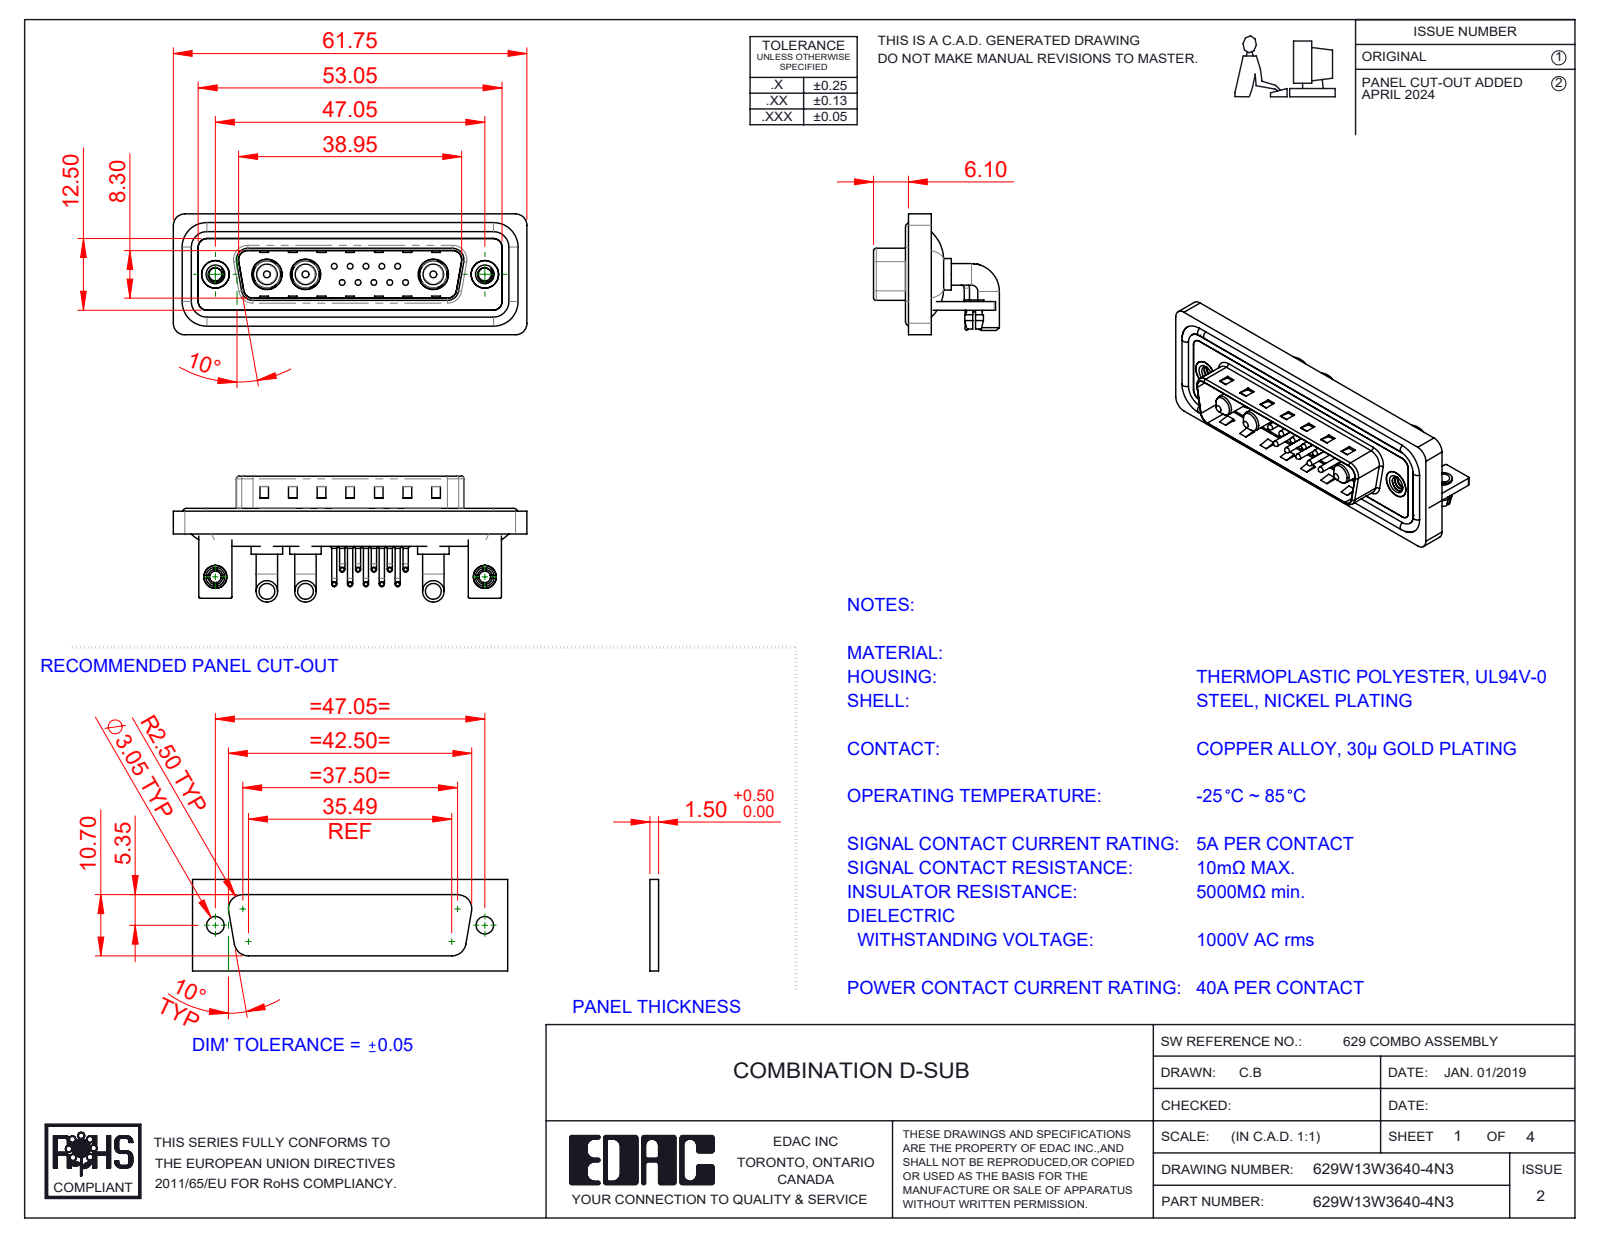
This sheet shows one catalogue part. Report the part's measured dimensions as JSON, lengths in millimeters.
{"part_name": "629Combo Contact Row 2; 629Combo Shell Rear_25 Contacts; Power Pin_40A RA; 629Combo Stabilizer Bracket (+7 more)", "step_written_by": "SolidWorks 2023 (CONFIG_CONTROL_DESIGN)", "units": "millimeters", "bodies": {"solids": 27, "faces": 1844, "planar": 947, "cylindrical": 661, "other": 236}, "overall_size": [61.75, 21.98, 21.1], "volume_mm3": 8143, "surface_area_mm2": 13425, "round_holes": [[2, 12], [0.75, 10], [1.6, 10], [4.85, 3], [5.3, 3], [2.26, 2], [2.5, 2], [3.2, 2], [4, 2], [4.8, 2], [5, 2]], "round_bosses_or_shafts": [[0.9, 20], [1.5, 10], [1, 10], [0.65, 10], [3.75, 6], [1.6, 4], [5.5, 3], [5.2, 3]], "partial_cylinders_radius": [[2, 19], [1.5, 18], [0.25, 16], [1.01, 10], [0.5, 9], [1.6, 8], [0.6, 4], [0.65, 4]], "face_to_face_distances": [0.4, 0.8, 1.5, 2.9, 2.1, 1.1, 4.1, 1.6, 3.7, 4.5], "hole_center_spacings": [3.16, 2.77, 5.04, 5.54, 7.49, 5.03, 8.31, 10.11]}
